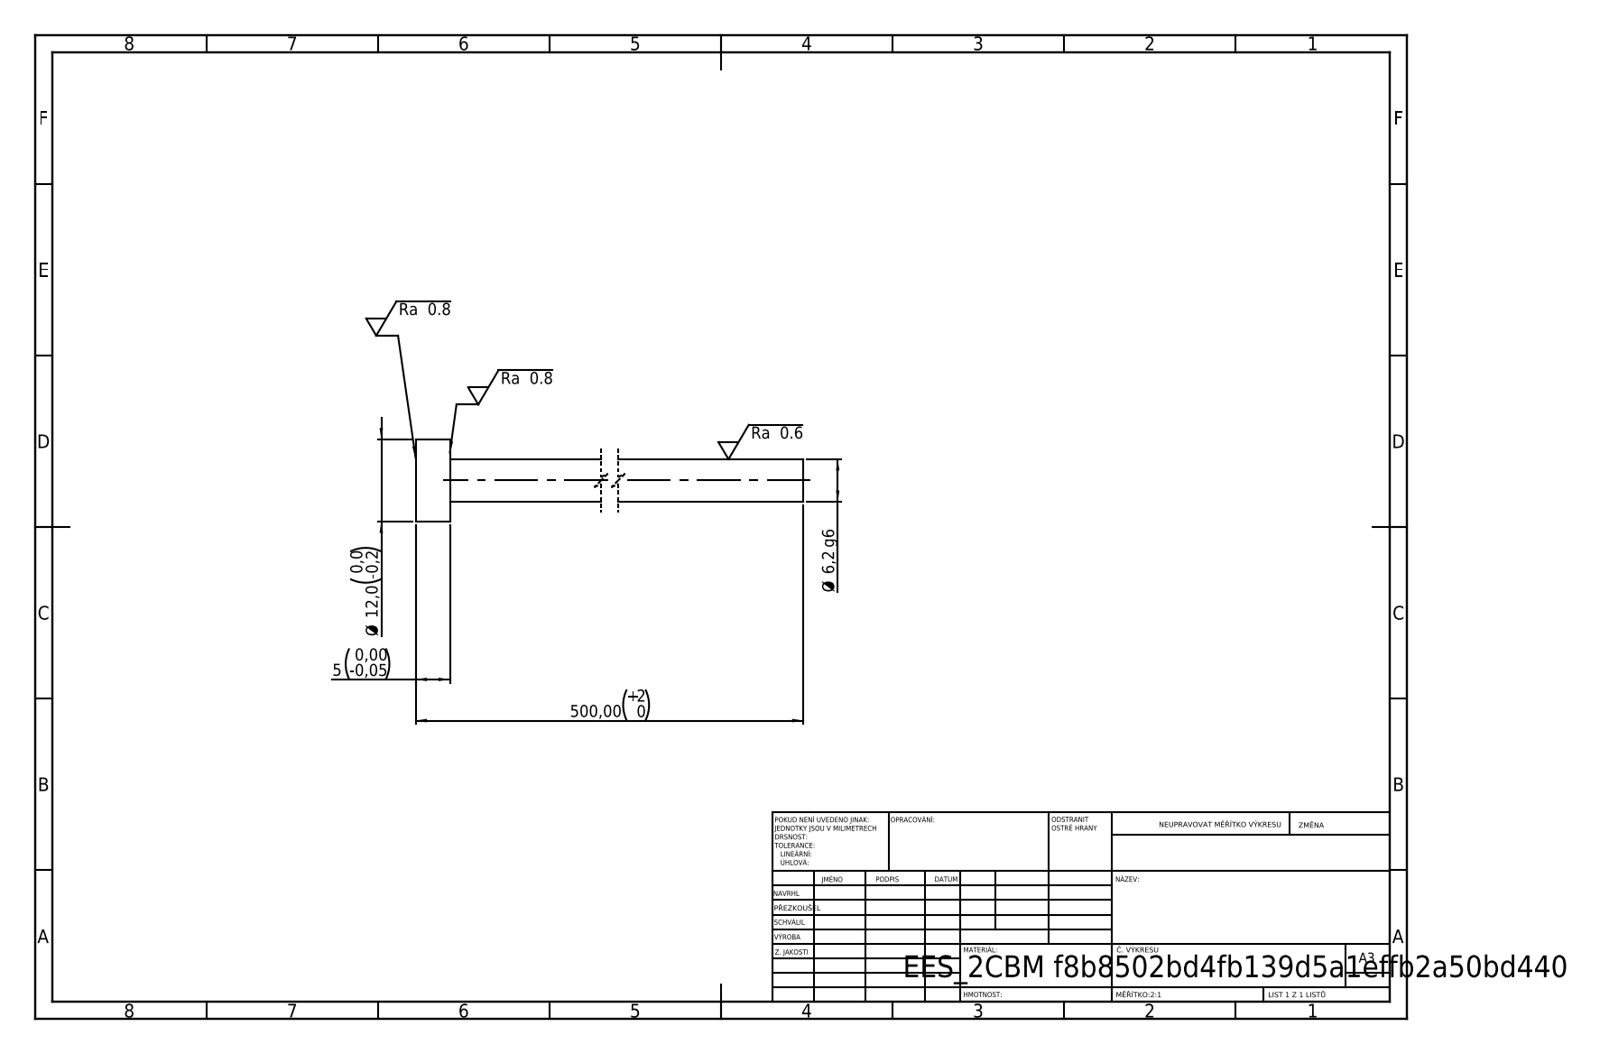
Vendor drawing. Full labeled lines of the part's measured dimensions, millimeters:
STEP written by: SolidWorks 2019 (CONFIG_CONTROL_DESIGN)
Units: millimetres
Bodies: 1 solid, 7 faces (3 planar, 4 cylindrical, 0 other)
Overall size (bounding box): 500 × 12 × 12
Volume: 15 510 mm³ · Surface area: 10 056 mm²
Round bosses / shafts (diameter × count): ⌀12 ×1, ⌀6.2 ×1
Main face-to-face distances: 5, 500, 495
